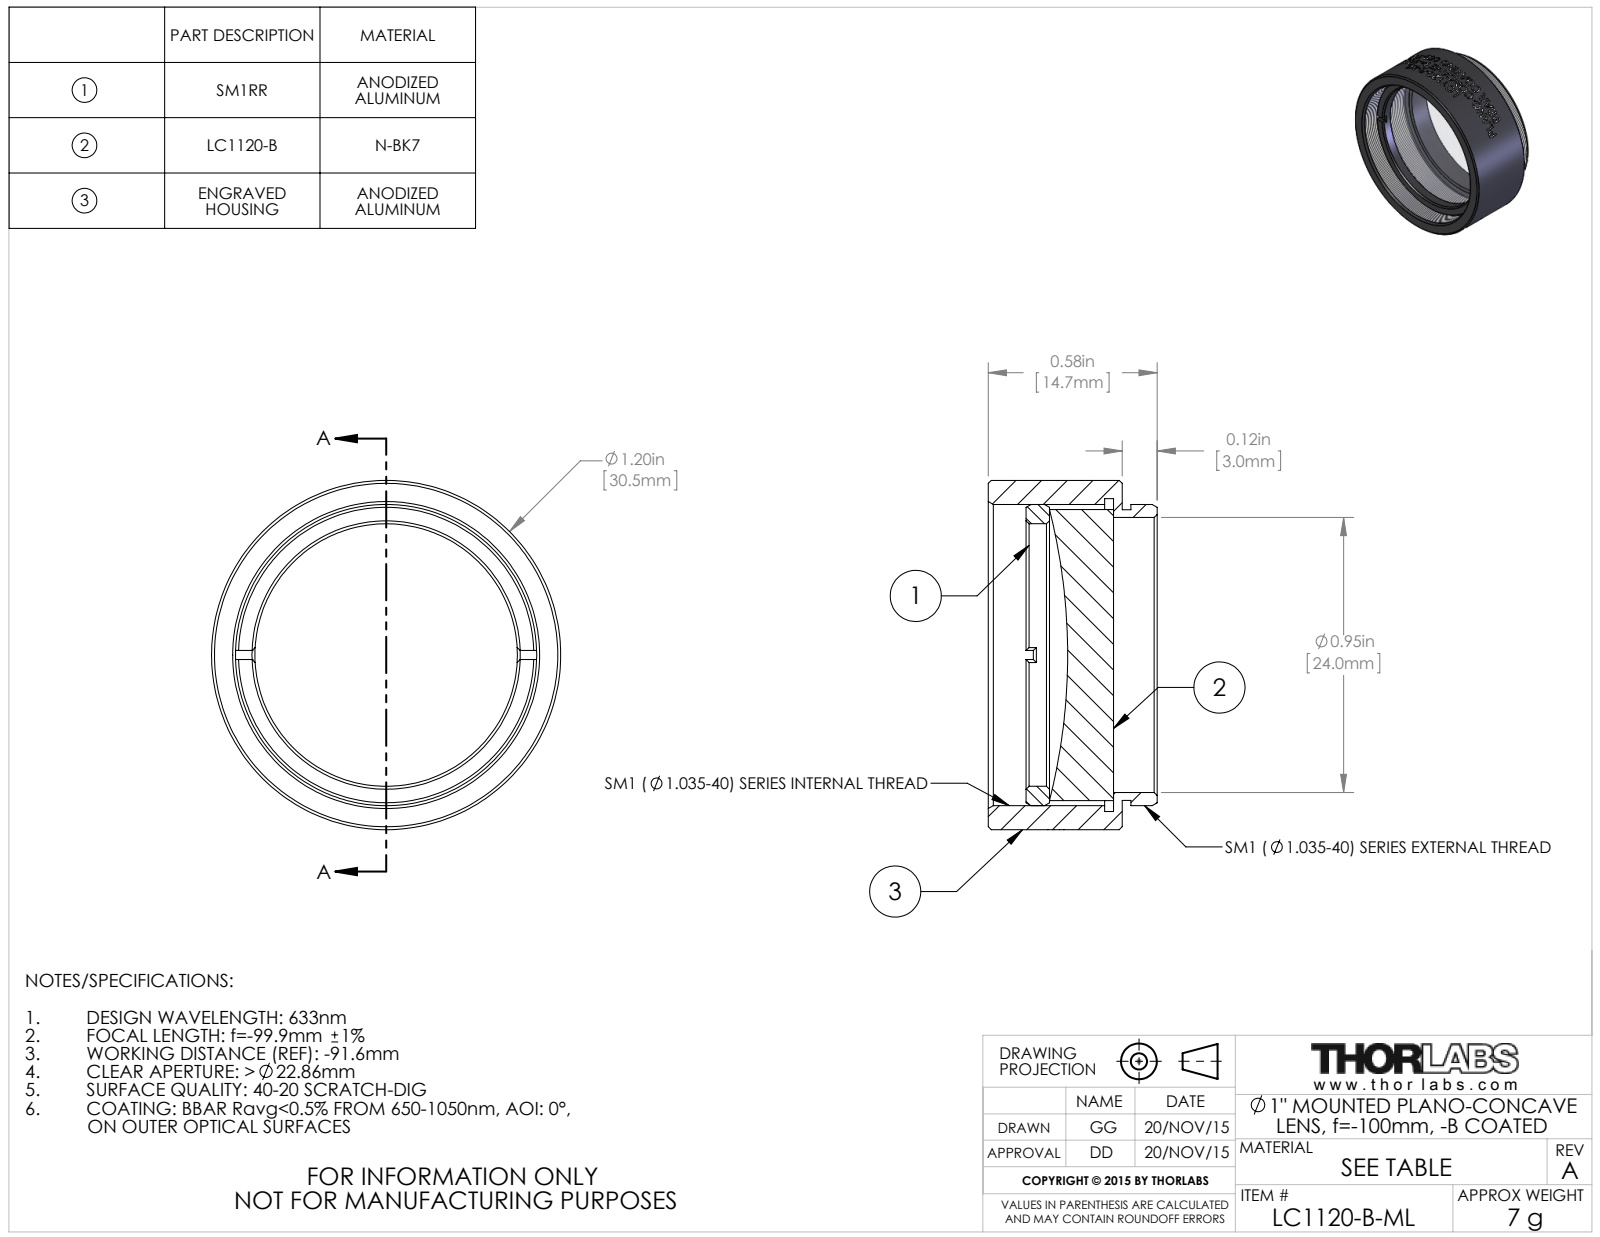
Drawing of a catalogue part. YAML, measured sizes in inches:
part_name: "TTN045316-E0W"
step_written_by: "SolidWorks 2014 (CONFIG_CONTROL_DESIGN)"
units: inches
bodies: {solids: 3, faces: 155, planar: 20, cylindrical: 111, other: 24}
overall_size: [1.2, 1.2, 0.58]
volume: 0.313
surface_area: 8.054
round_holes:
  - {diameter: 0.902, count: 1}
  - {diameter: 0.945, count: 1}
  - {diameter: 1.075, count: 1}
round_bosses_or_shafts:
  - {diameter: 1.2, count: 1}
  - {diameter: 1.035, count: 1}
  - {diameter: 1, count: 1}
  - {diameter: 0.999, count: 1}
face_to_face_distances: [0.03, 0.46, 0.43, 0.25, 0.22, 0.21, 0.33, 0.3, 0.08, 0.13]
